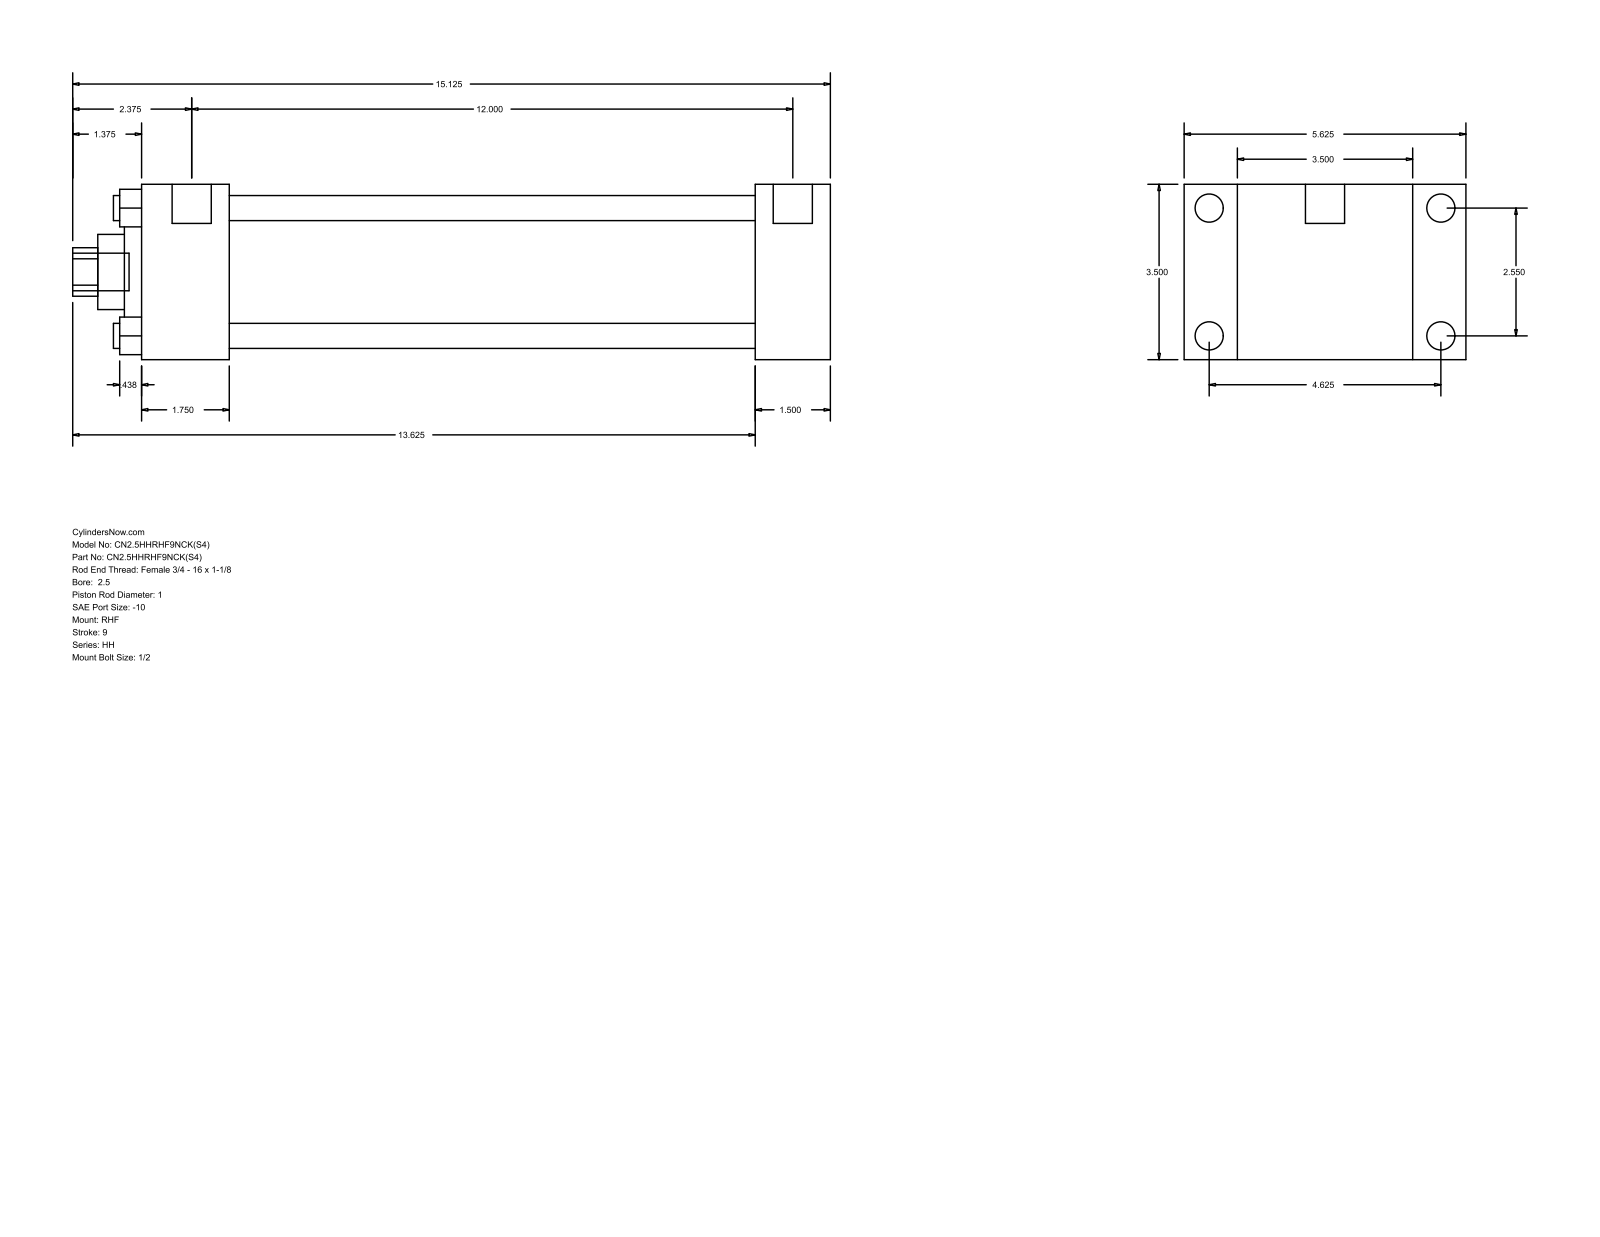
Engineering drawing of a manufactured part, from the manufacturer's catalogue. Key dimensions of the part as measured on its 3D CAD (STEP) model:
Part name (STEP PRODUCT): HH_RHF__0250_1
STEP written by: GSSL Pune (CONFIG_CONTROL_DESIGN)
Units: millimetres
Bodies: 0 solids, 90 faces (61 planar, 29 cylindrical, 0 other)
Overall size (bounding box): 384.18 × 142.88 × 88.9
Round holes (diameter × count): ⌀12.7 ×4, ⌀25.4 ×1, ⌀38.1 ×1, ⌀60.33 ×1, ⌀73.03 ×1
Round bosses / shafts (diameter × count): ⌀14.3 ×4, ⌀5.56 ×4, ⌀19.84 ×2, ⌀19.05 ×1
Partial cylindrical surfaces — rounded edges, fillets, slot ends (radius × count): R12.29 ×1
Main face-to-face distances: 88.9, 38.11, 26.99, 115.89, 311.15, 349.26, 142.88, 44.46, 266.69, 304.8
Hole centre spacings: 45.79, 64.76, 91.58
